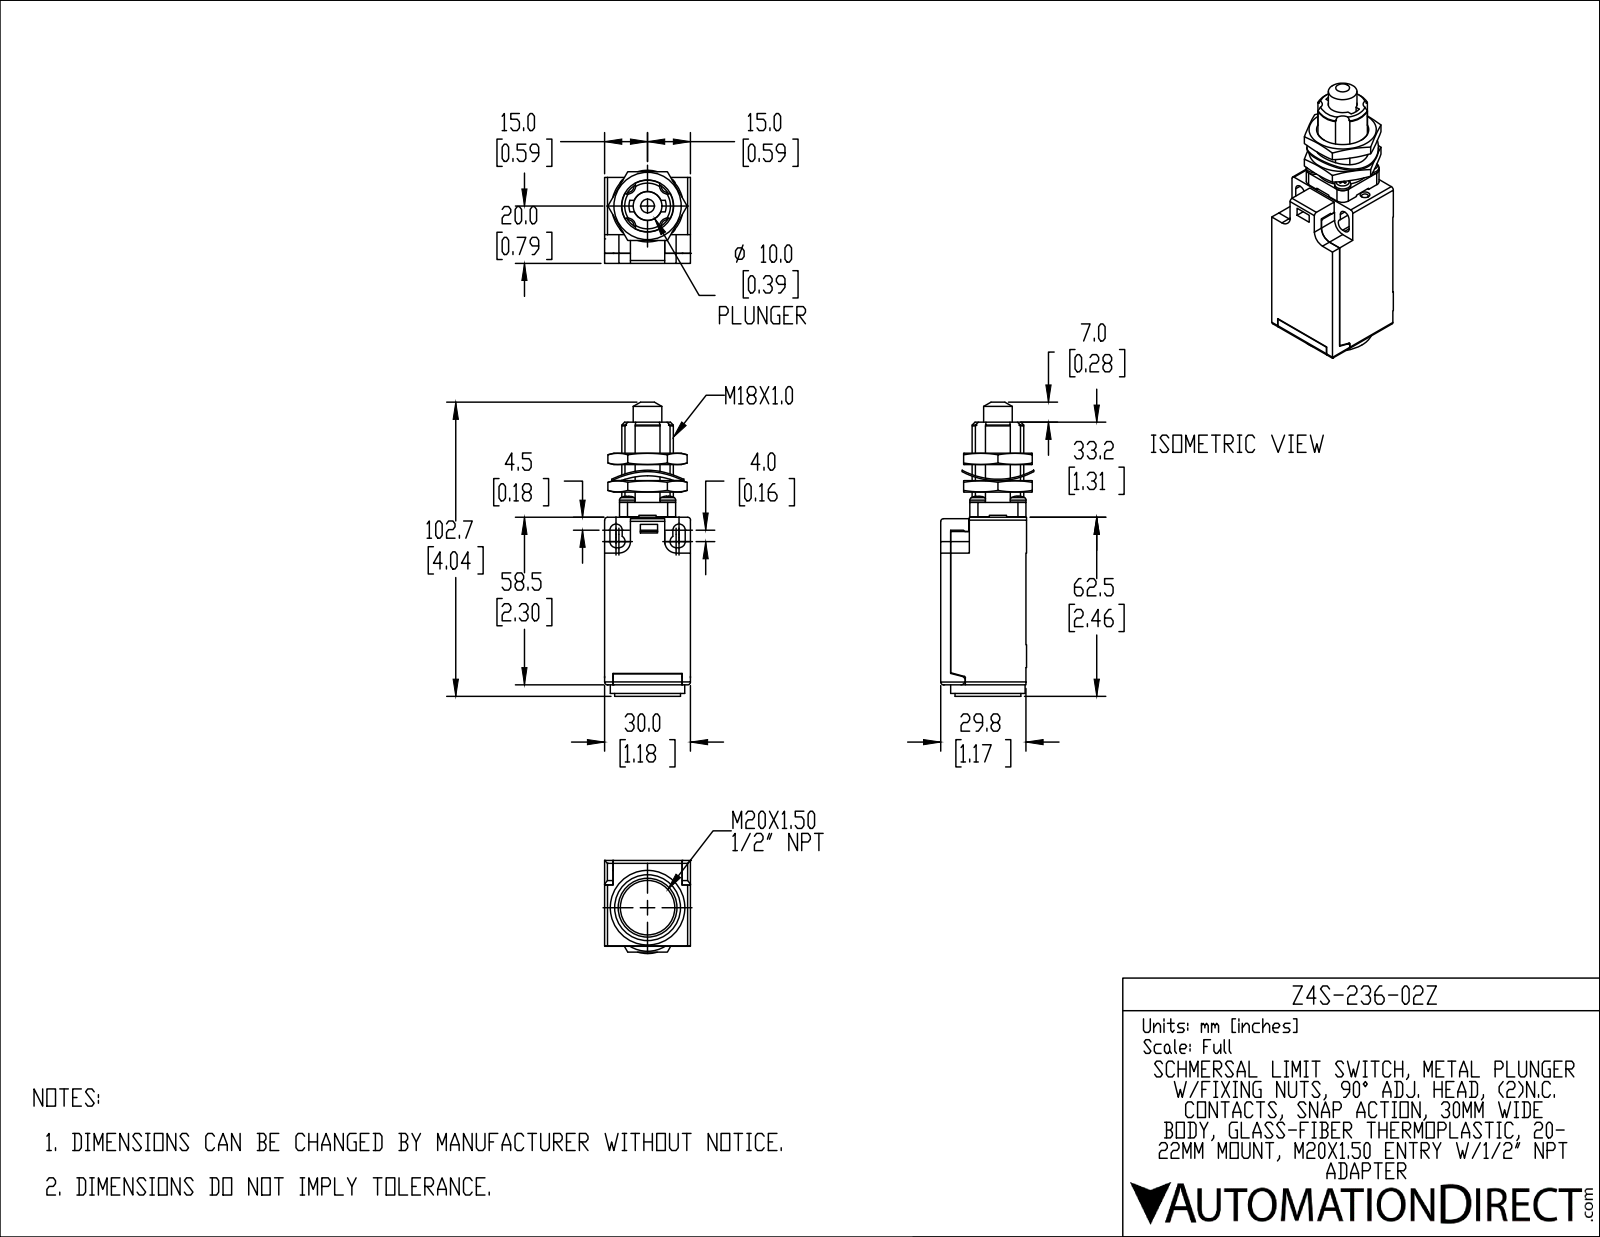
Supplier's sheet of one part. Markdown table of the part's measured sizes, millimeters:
| quantity | value |
| --- | --- |
| part name | Z4S-236-02Z |
| STEP written by | SolidWorks 2019 (AUTOMOTIVE_DESIGN) |
| units | millimeters |
| bodies | 4 solids, 348 faces (226 planar, 90 cylindrical, 32 other) |
| overall size | 102.7 × 32.5 × 30 |
| volume | 57 780 mm³ |
| surface area | 20 270 mm² |
| round holes (diameter × count) | 2.4 × 6, 3.2 × 4, 13 × 1, 13.8 × 1, 18.6 × 1, 19 × 1 |
| round bosses / shafts (diameter × count) | 5.4 × 4, 26 × 1, 25 × 1, 23 × 1, 10.5 × 1, 10 × 1, 6.3 × 1 |
| partial cylindrical surfaces (radius × count) | 1 × 6, 2.2 × 6, 2.8 × 4, 2.8 × 4, 4 × 2, 26.5 × 2, 0.6 × 1, 1.5 × 1 |
| main face-to-face distances | 30, 3.5, 26.3, 29.8, 4, 26.5, 2.2, 2, 52.5, 3 |
| hole center spacings | 8.1, 9.9, 14, 19.3, 7.8, 11, 11.5, 12.6 |
